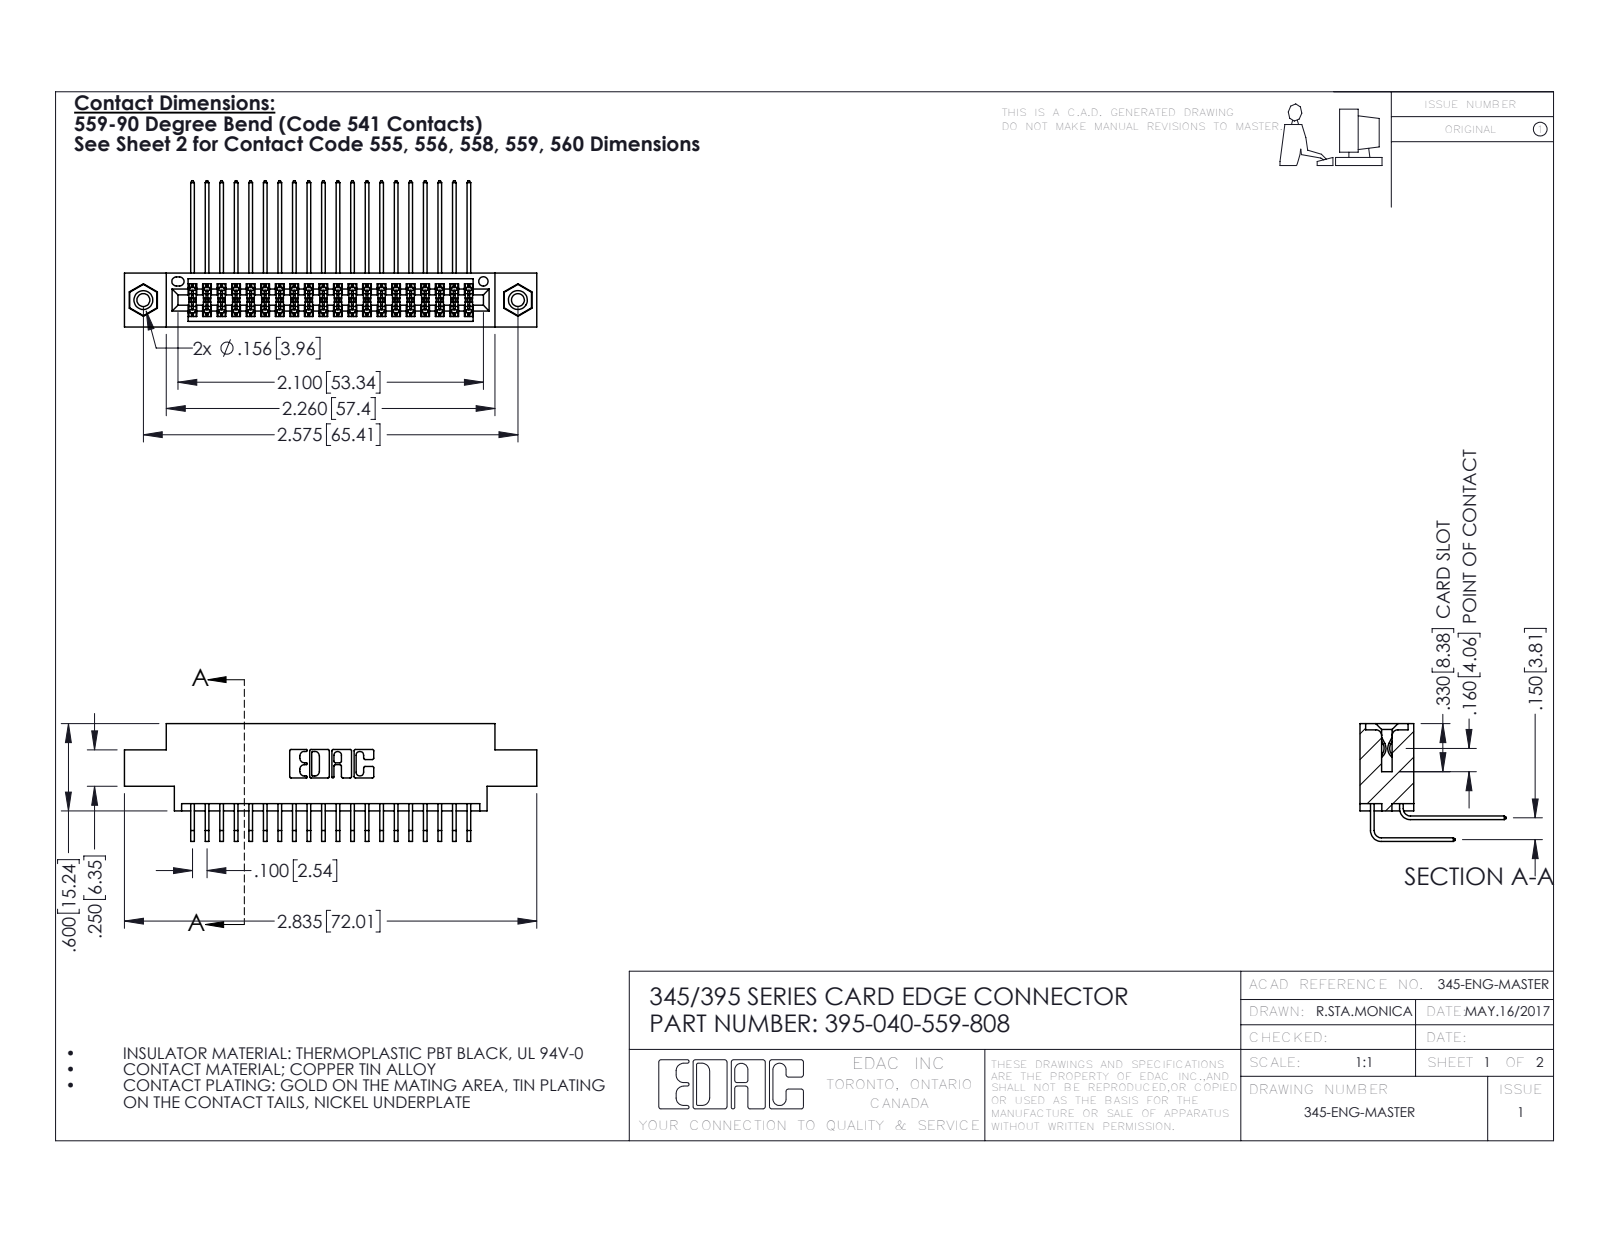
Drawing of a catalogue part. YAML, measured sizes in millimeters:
part_name: "345-250-001_345-250-003-102; 395-040-559-808; 345-292-001_559 Tail - 2; 345-292-001_558 559 Tail - 1 (+1 more)"
step_written_by: "SolidWorks 2016 (CONFIG_CONTROL_DESIGN)"
units: millimeters
bodies: {solids: 43, faces: 2270, planar: 1516, cylindrical: 738, other: 16}
overall_size: [72, 25.5, 20.5]
volume: 6900
surface_area: 11020
round_holes:
  - {diameter: 2.3, count: 2}
  - {diameter: 3.2, count: 2}
  - {diameter: 4, count: 2}
  - {diameter: 1.6, count: 1}
round_bosses_or_shafts:
  - {diameter: 3.9, count: 2}
partial_cylinders:
  - {radius: 0.2, count: 60}
  - {radius: 0.3, count: 22}
  - {radius: 0.2, count: 6}
  - {radius: 0.8, count: 6}
  - {radius: 0.7, count: 3}
  - {radius: 0.4, count: 2}
  - {radius: 0.5, count: 2}
  - {radius: 0.6, count: 2}
face_to_face_distances: [1.8, 7.6, 9.4, 5.1, 2.5, 6.9, 0.6, 3.8, 5.7, 4.4]
hole_center_spacings: [6.9, 59.5, 65.4]
